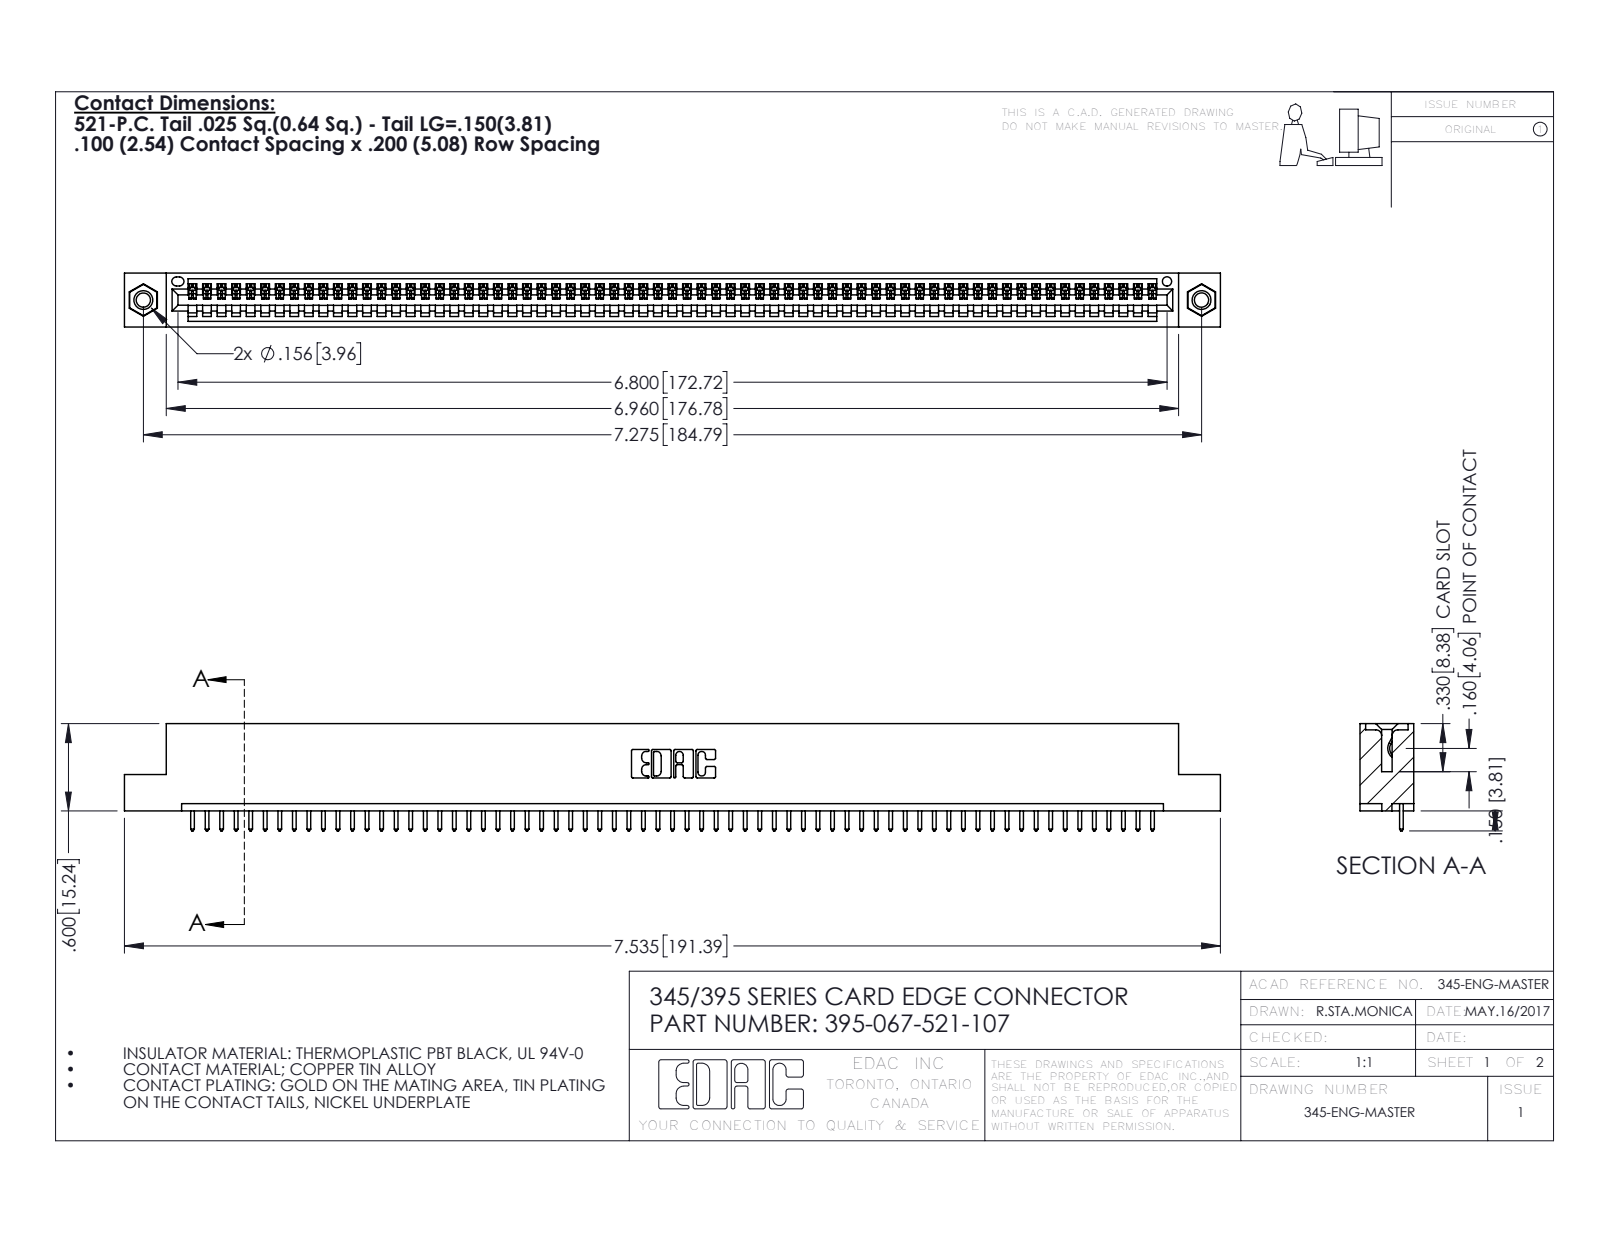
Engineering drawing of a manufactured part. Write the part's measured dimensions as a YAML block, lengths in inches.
part_name: "395-067-521-107; 345-250-001_345-250-005-103; 345-292-001_345-293-121; 345 Part_Flush Mounting Lugs - 0.156 Dia-TI"
step_written_by: "SolidWorks 2016 (CONFIG_CONTROL_DESIGN)"
units: inches
bodies: {solids: 70, faces: 4072, planar: 2792, cylindrical: 1264, other: 16}
overall_size: [7.535, 0.737, 0.37]
volume: 1.109
surface_area: 36.87
round_holes:
  - {diameter: 0.098, count: 2}
  - {diameter: 0.125, count: 2}
  - {diameter: 0.156, count: 2}
  - {diameter: 0.064, count: 1}
round_bosses_or_shafts:
  - {diameter: 0.155, count: 2}
partial_cylinders:
  - {radius: 0.006, count: 134}
  - {radius: 0.01, count: 134}
  - {radius: 0.01, count: 22}
  - {radius: 0.007, count: 6}
  - {radius: 0.031, count: 6}
  - {radius: 0.026, count: 3}
  - {radius: 0.031, count: 2}
  - {radius: 0.04, count: 2}
face_to_face_distances: [0.072, 0.298, 0.37, 0.2, 0.098, 0.272, 0.025, 0.225, 0.149, 0.072]
hole_center_spacings: [0.27, 7.039, 7.275]
